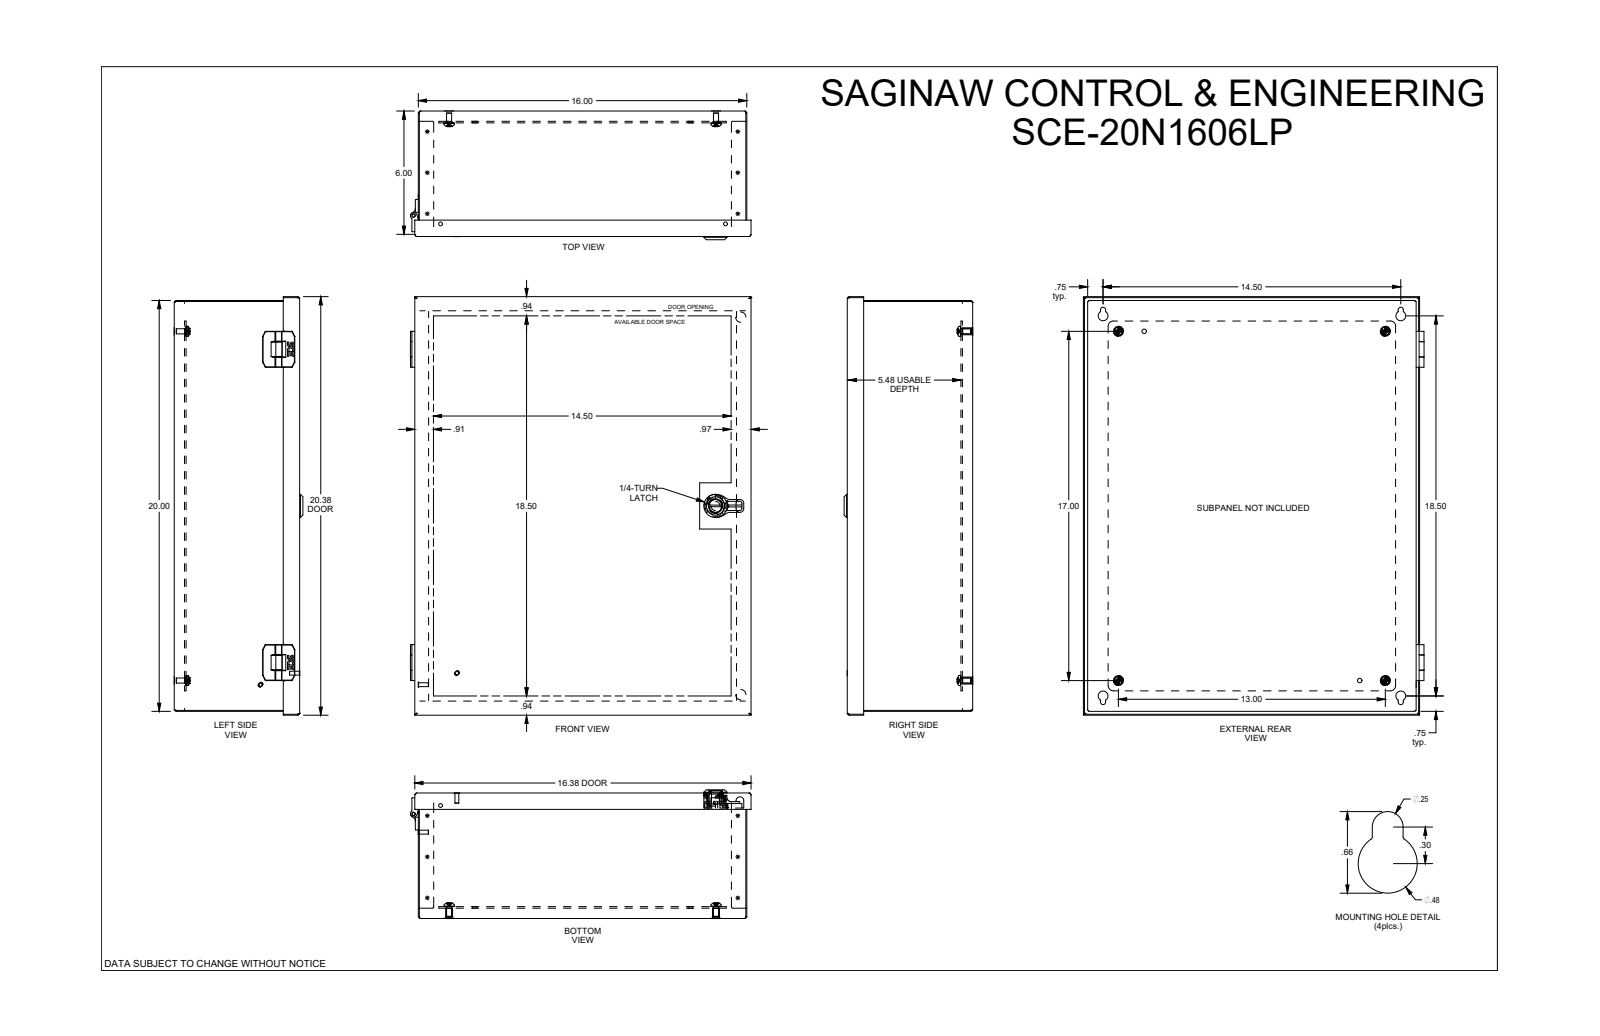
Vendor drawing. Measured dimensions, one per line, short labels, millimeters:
name: SCE-20N1606LP
written by: SolidWorks 2019 (CONFIG_CONTROL_DESIGN)
unit: mm
bodies: 0 solids, 3058 faces (1038 planar, 1032 cylindrical, 988 other)
size: 517.5 × 421.5 × 159.2
holes: 4× ⌀6.4, 4× ⌀7.1, 4× ⌀8.4, 4× ⌀8.7, 4× ⌀12.2, 4× ⌀12.2, 2× ⌀4.7, 2× ⌀4.9, 2× ⌀5.5, 1× ⌀4, 1× ⌀11.2, 1× ⌀16.1
bosses: 4× ⌀12.5, 4× ⌀8.7, 4× ⌀6.3, 4× ⌀6, 4× ⌀4.3, 4× ⌀4.1, 4× ⌀3.4, 4× ⌀2.7
rounds: 253× R0.3, 132× R2.7, 130× R0.1, 103× R0.5, 32× R0.4, 24× R0.6, 16× R1.2, 16× R2.4
face distances: 1.2, 153.9, 152.7, 155.1, 12.7, 11.5, 14.6, 13.4, 139.3, 140.5
hole spacings: 26.9, 349.8, 451.3, 570.3, 27.7, 31.8, 54.3, 215.9
